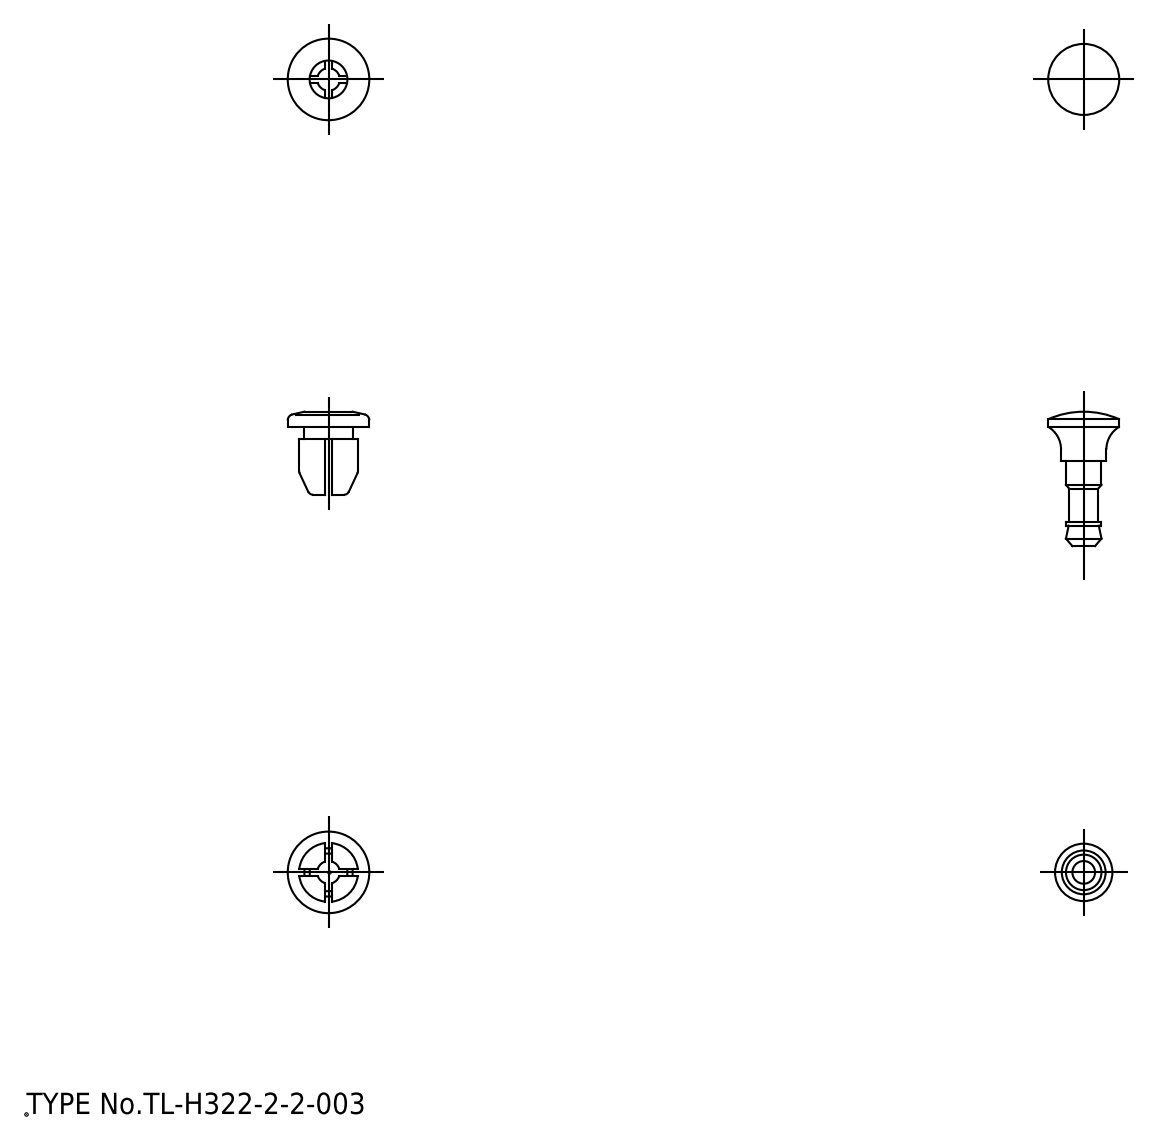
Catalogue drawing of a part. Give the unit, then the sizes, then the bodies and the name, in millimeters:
Units: millimetres
Overall size (bounding box): 19.2 × 10.9 × 10.9
Round holes (diameter × count): ⌀5 ×1
Round bosses / shafts (diameter × count): ⌀10.9 ×1, ⌀9.4 ×1, ⌀7.8 ×1, ⌀6.4 ×1, ⌀6 ×1, ⌀4.7 ×1, ⌀3.8 ×1
Partial cylindrical surfaces — rounded edges, fillets, slot ends (radius × count): R1.5 ×1
Main face-to-face distances: 1, 1.6, 6, 7.6, 9.6, 3.6, 2, 11.3, 5.3, 3.7
Volume: 713 mm³ · Surface area: 996 mm²
Bodies: 2 solids, 80 faces (30 planar, 24 cylindrical, 26 other)
Part name (STEP PRODUCT): grommet; plunger
STEP written by: spGate 18.9.1 (****-****-****-****) (AUTOMOTIVE_DESIGN)
